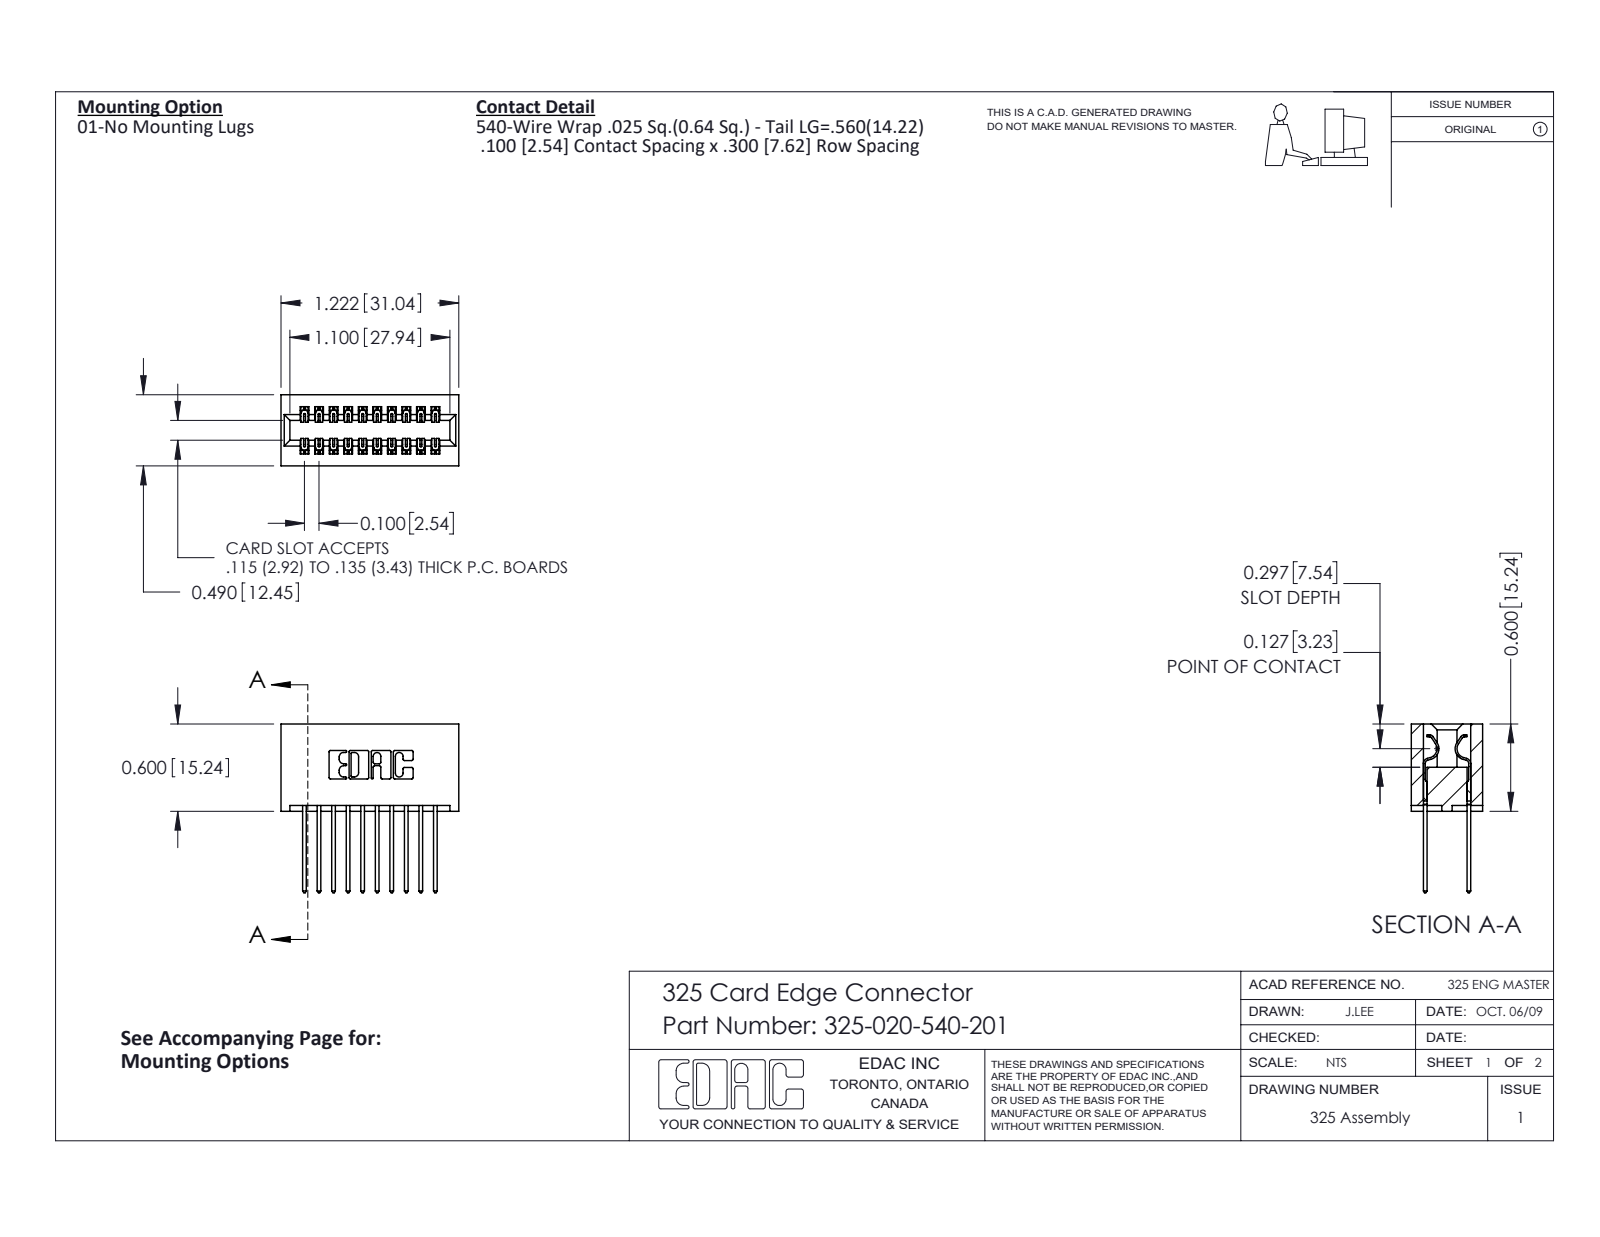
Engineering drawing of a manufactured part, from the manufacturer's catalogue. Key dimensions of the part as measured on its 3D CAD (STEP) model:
Part name (STEP PRODUCT): 325-292-001_325-293-140; 325-020-540-201; 325 Part_Lugless
STEP written by: SolidWorks 2016 (CONFIG_CONTROL_DESIGN)
Units: inches
Bodies: 21 solids, 1146 faces (786 planar, 360 cylindrical, 0 other)
Overall size (bounding box): 1.222 × 1.16 × 0.49
Volume: 0.269 in³ · Surface area: 8.666 in²
Partial cylindrical surfaces — rounded edges, fillets, slot ends (radius × count): R0.006 ×30, R0.01 ×22, R0.01 ×20, R0.007 ×6, R0.031 ×6, R0.026 ×3, R0.014 ×2, R0.022 ×2
Main face-to-face distances: 0.3, 0.083, 0.407, 0.1, 0.2, 0.107, 0.383, 0.025, 0.4, 0.49
